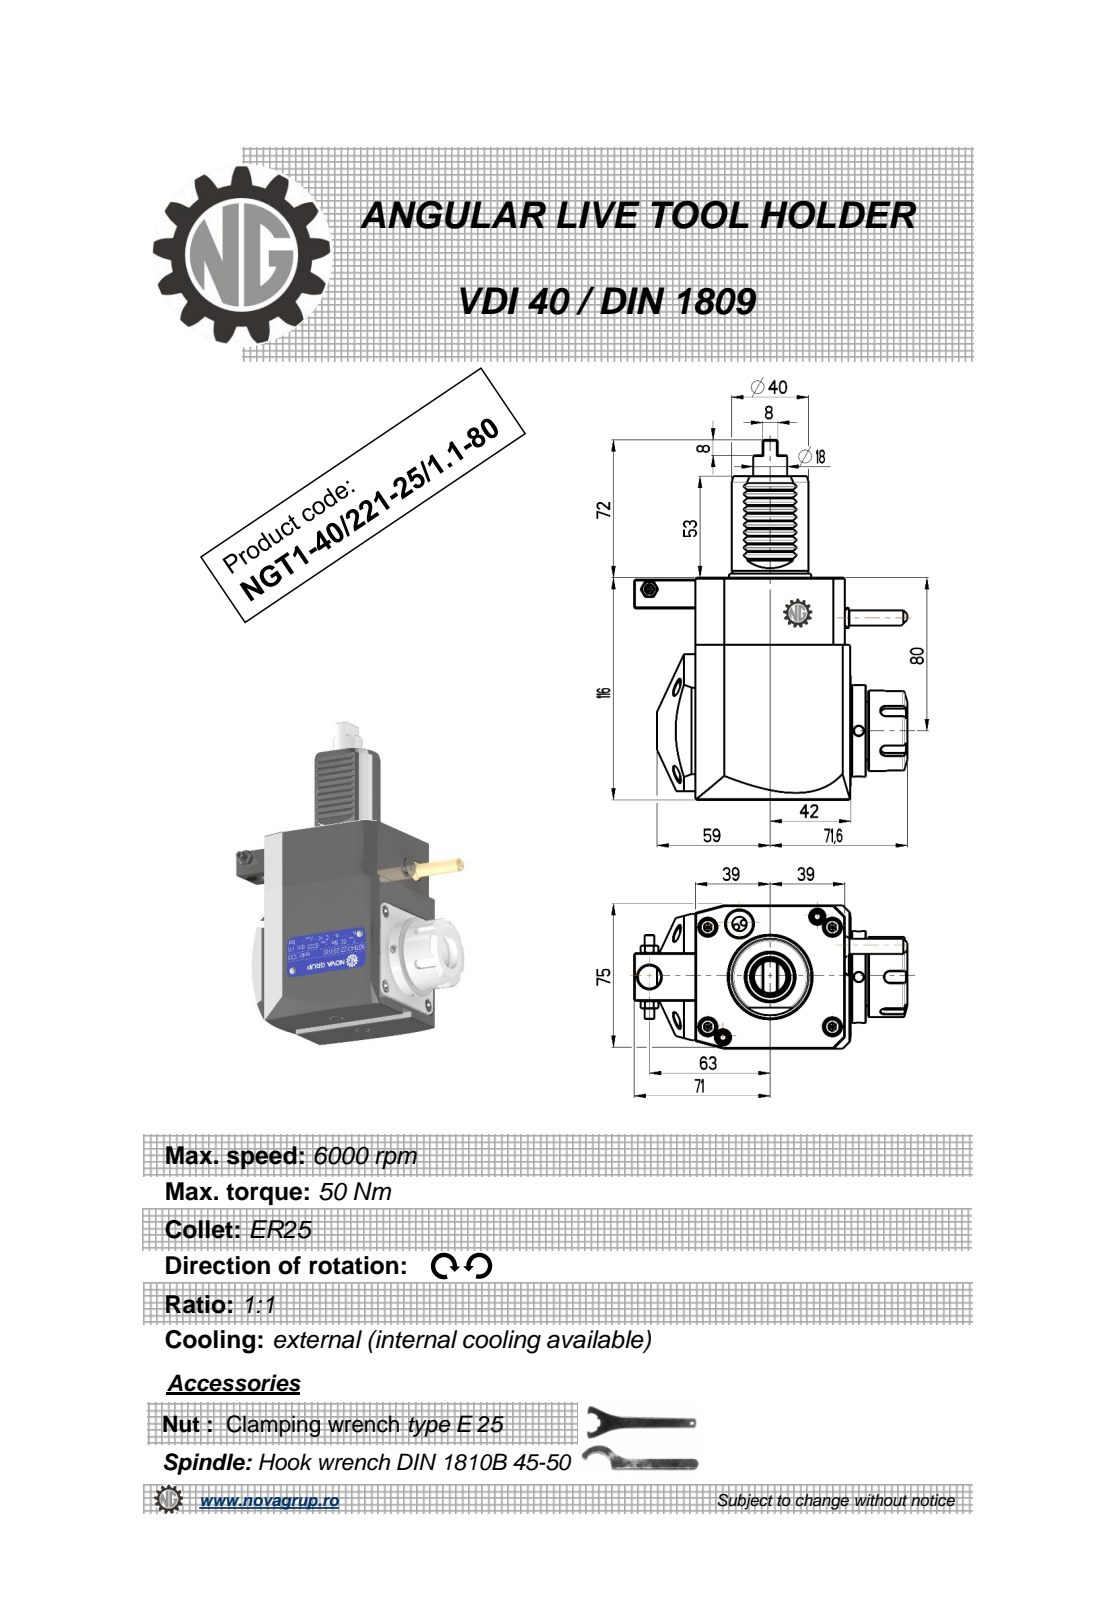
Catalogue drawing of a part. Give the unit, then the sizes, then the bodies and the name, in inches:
Units: inches
Overall size (bounding box): 7.402 × 5.614 × 3.016
Round holes (diameter × count): ⌀0.197 ×3, ⌀0.118 ×1, ⌀0.165 ×1, ⌀0.374 ×1, ⌀0.472 ×1, ⌀0.799 ×1
Round bosses / shafts (diameter × count): ⌀1.89 ×1, ⌀1.654 ×1, ⌀1.575 ×1, ⌀1.496 ×1, ⌀1.299 ×1, ⌀0.701 ×1, ⌀0.441 ×1, ⌀0.353 ×1
Partial cylindrical surfaces — rounded edges, fillets, slot ends (radius × count): R0.01 ×12, R0.012 ×10, R0.009 ×6, R0.118 ×5, R0.031 ×2, R0.02 ×1, R1.575 ×1
Main face-to-face distances: 2.953, 4.567, 3.189, 0.118, 3.071, 3.181, 0.11, 0.315, 0.433, 0.984
Hole centre spacings: 0.824, 2.407, 2.854, 4.301, 5.195
Volume: 52.15 in³ · Surface area: 107.3 in²
Bodies: 1 solid, 438 faces (200 planar, 89 cylindrical, 149 other)
Part name (STEP PRODUCT): NGT1_40_221_25_1_1_80
STEP written by: PRO/ENGINEER BY PARAMETRIC TECHNOLOGY CORPORATION, 2010280 (CONFIG_CONTROL_DESIGN)
